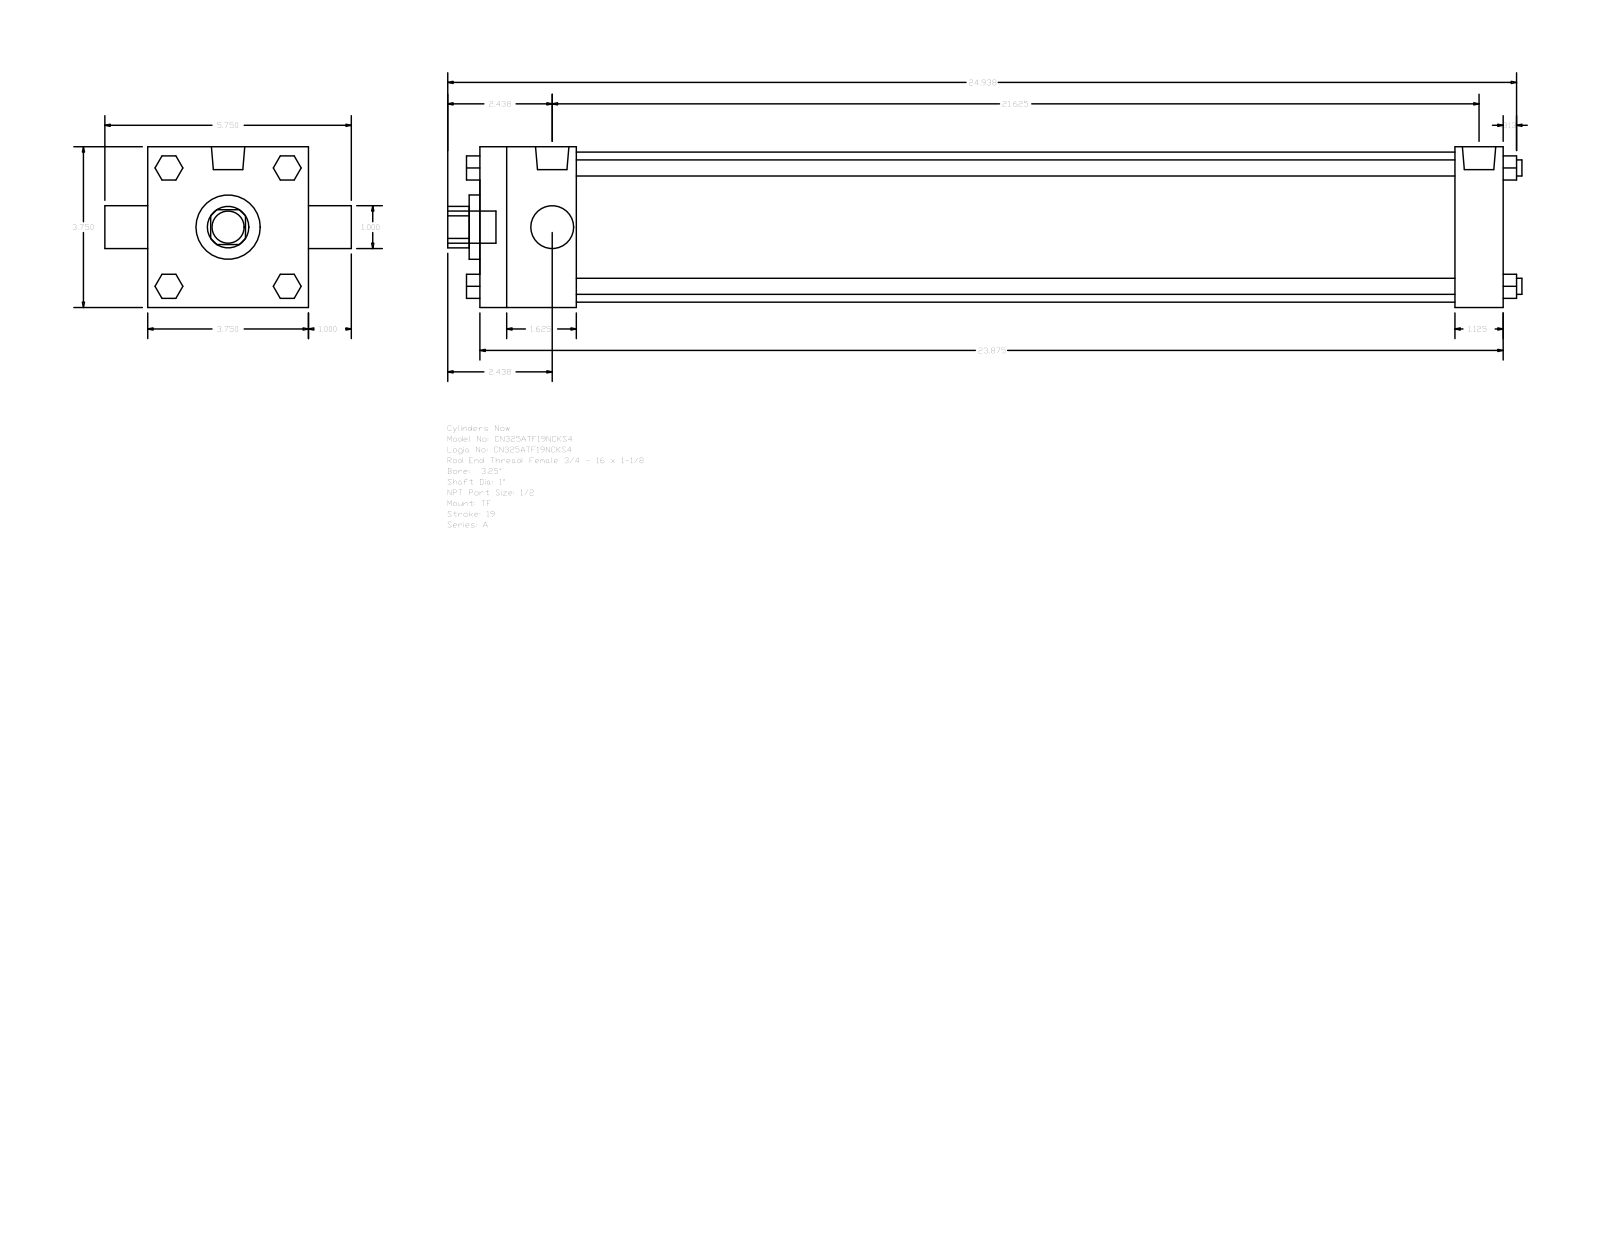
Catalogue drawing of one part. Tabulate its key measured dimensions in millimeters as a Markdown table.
| quantity | value |
| --- | --- |
| part name | A_TF__0325_1 |
| STEP written by | GSSL Pune (CONFIG_CONTROL_DESIGN) |
| units | millimeters |
| bodies | 0 solids, 120 faces (92 planar, 28 cylindrical, 0 other) |
| overall size | 636.59 × 146.05 × 95.25 |
| round holes (diameter × count) | 25.4 × 2, 38.1 × 1, 88.9 × 1 |
| round bosses / shafts (diameter × count) | 9.53 × 4, 8.73 × 3, 19.77 × 2, 19.05 × 1 |
| partial cylindrical surfaces (radius × count) | 12.29 × 1 |
| main face-to-face distances | 95.24, 606.43, 57.15, 577.85, 520.7, 549.28, 28.58, 14.28, 35.05, 60.71 |
